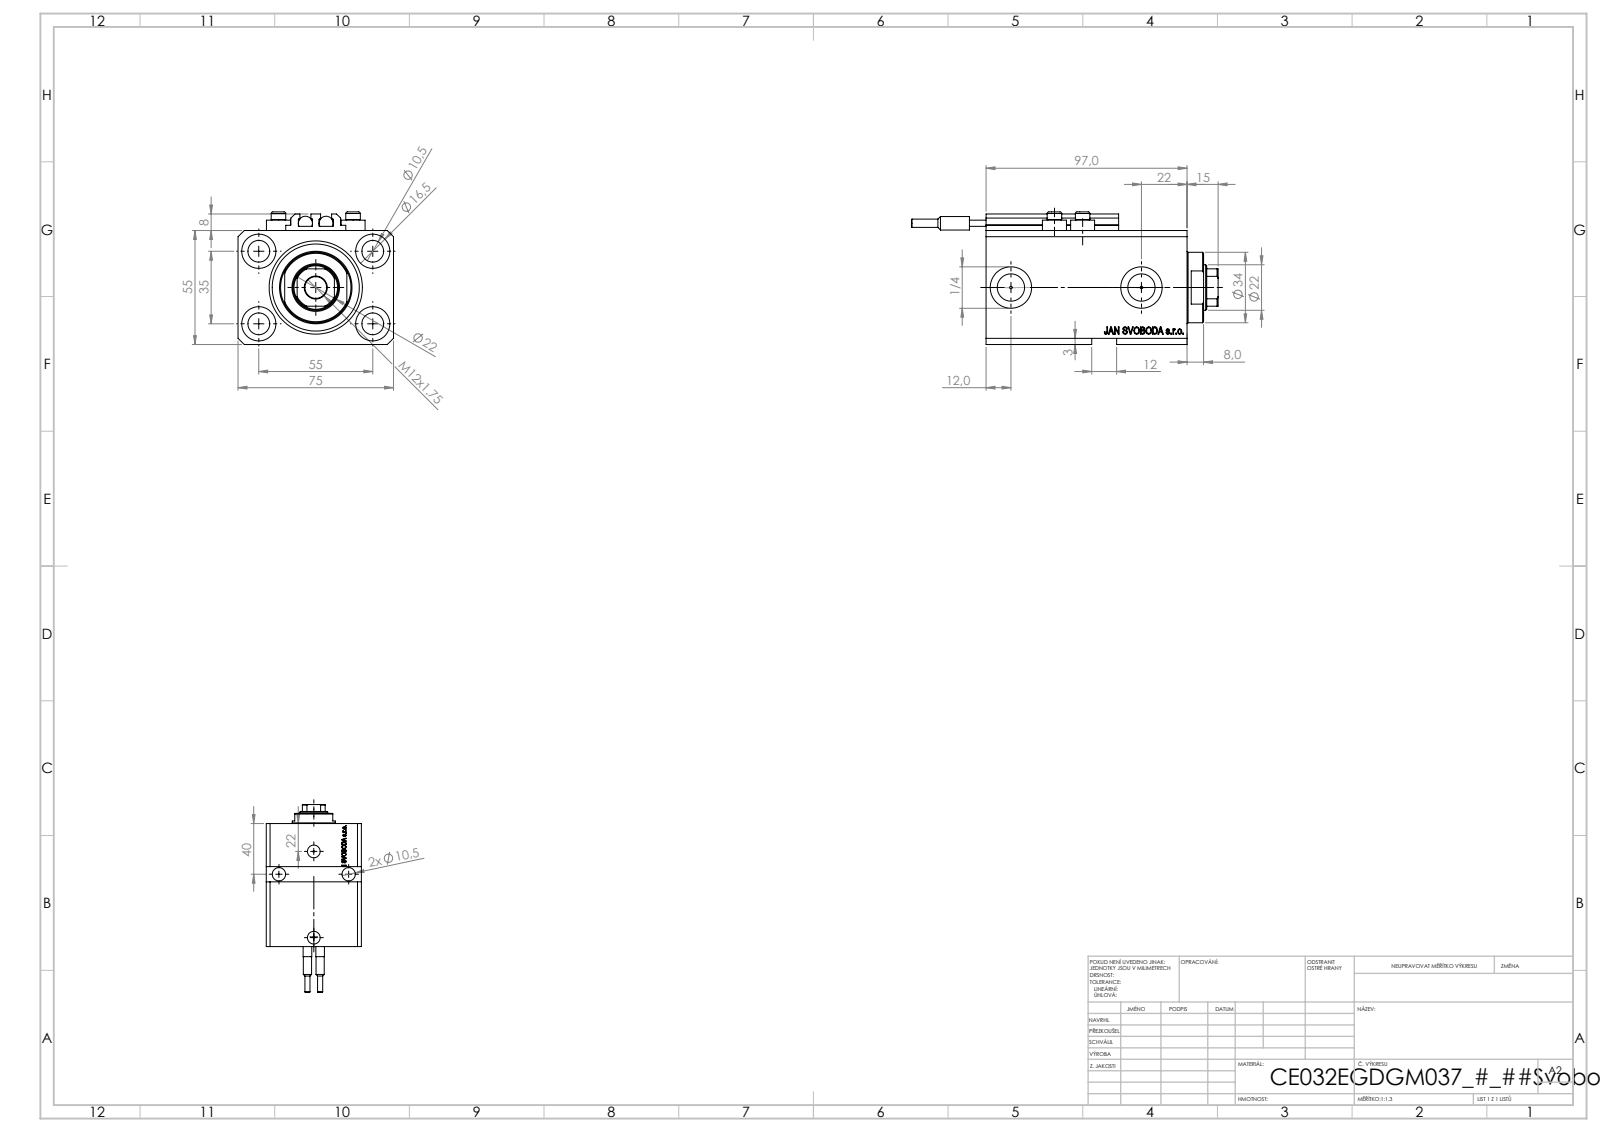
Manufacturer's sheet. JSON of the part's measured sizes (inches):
{"part_name": "SWITCH_V250CE; V250CE_VC_E; V250CE_C_VCP; ALLEN BOLT V250CE (+1 more)", "step_written_by": "SolidWorks 2019 (CONFIG_CONTROL_DESIGN)", "units": "inches", "bodies": {"solids": 10, "faces": 1132, "planar": 550, "cylindrical": 150, "other": 432}, "overall_size": [5.827, 2.953, 2.52], "volume_in3": 20.91, "surface_area_in2": 138.7, "round_holes": [[0.413, 7], [0.049, 4], [0.157, 4], [0.65, 4], [0.394, 2], [0.518, 2], [0.787, 2], [0.866, 1], [1.26, 1], [1.772, 1]], "round_bosses_or_shafts": [[0.457, 4], [0.276, 4], [0.268, 2], [0.256, 2], [0.157, 2], [1.339, 1]], "partial_cylinders_radius": [[0.008, 10], [0.413, 1]], "face_to_face_distances": [2.165, 2.953, 0.118, 0.591, 3.819, 3.228, 0.39, 2.244, 2.362, 2.047], "hole_center_spacings": [1.283, 2.165, 0.535, 0.555, 1.016, 1.228, 1.245, 1.294]}
